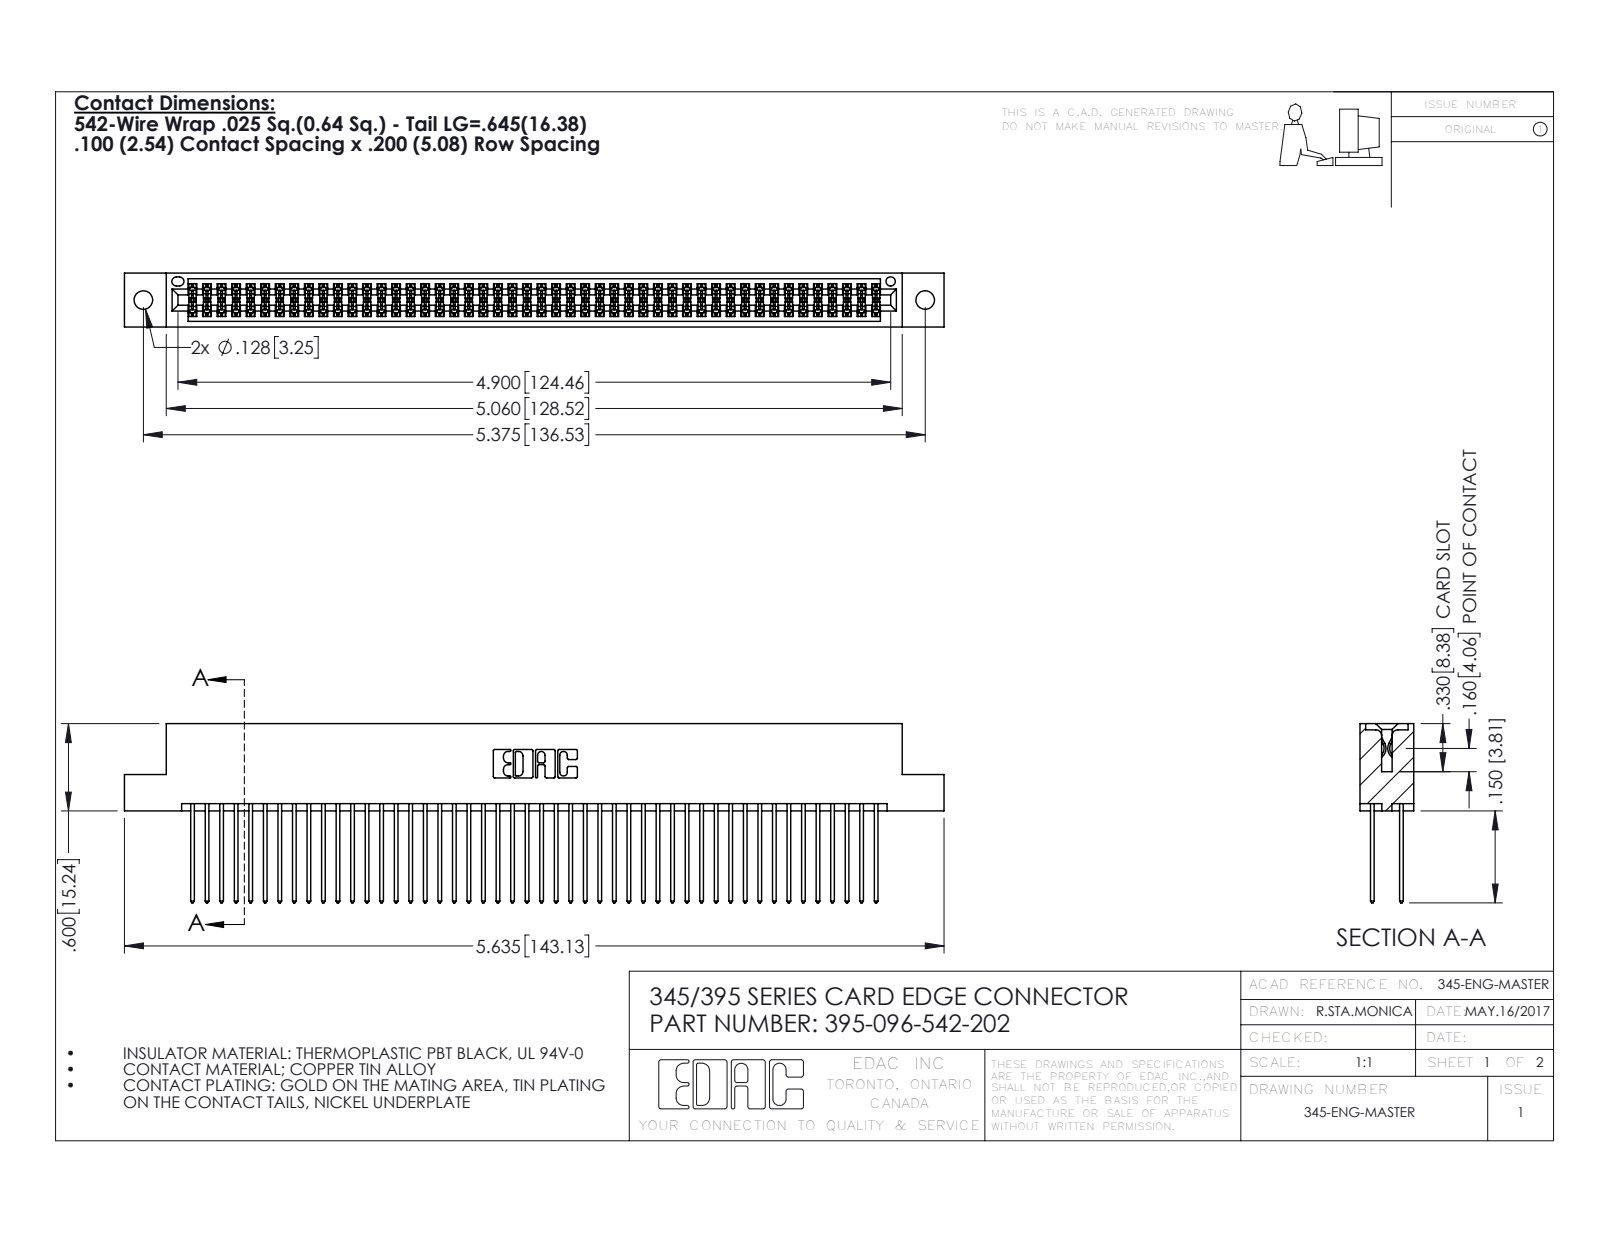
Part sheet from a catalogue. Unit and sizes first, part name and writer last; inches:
Units: inches
Overall size (bounding box): 5.635 × 1.232 × 0.37
Round holes (diameter × count): ⌀0.128 ×2, ⌀0.064 ×1
Partial cylindrical surfaces — rounded edges, fillets, slot ends (radius × count): R0.006 ×144, R0.01 ×96, R0.01 ×22, R0.007 ×6, R0.031 ×6, R0.026 ×3, R0.014 ×2, R0.019 ×2
Main face-to-face distances: 0.298, 0.072, 0.2, 0.098, 0.272, 0.025, 0.225, 0.37, 0.175, 0.149
Hole centre spacings: 0.27, 5.139, 5.375
Volume: 0.877 in³ · Surface area: 35.92 in²
Bodies: 97 solids, 4926 faces (3248 planar, 1678 cylindrical, 0 other)
Part name (STEP PRODUCT): 395-096-542-202; 345 Part_Flush Mounting Lugs - 0.128 Dia; 345-292-001_345-293-142
STEP written by: SolidWorks 2016 (CONFIG_CONTROL_DESIGN)
